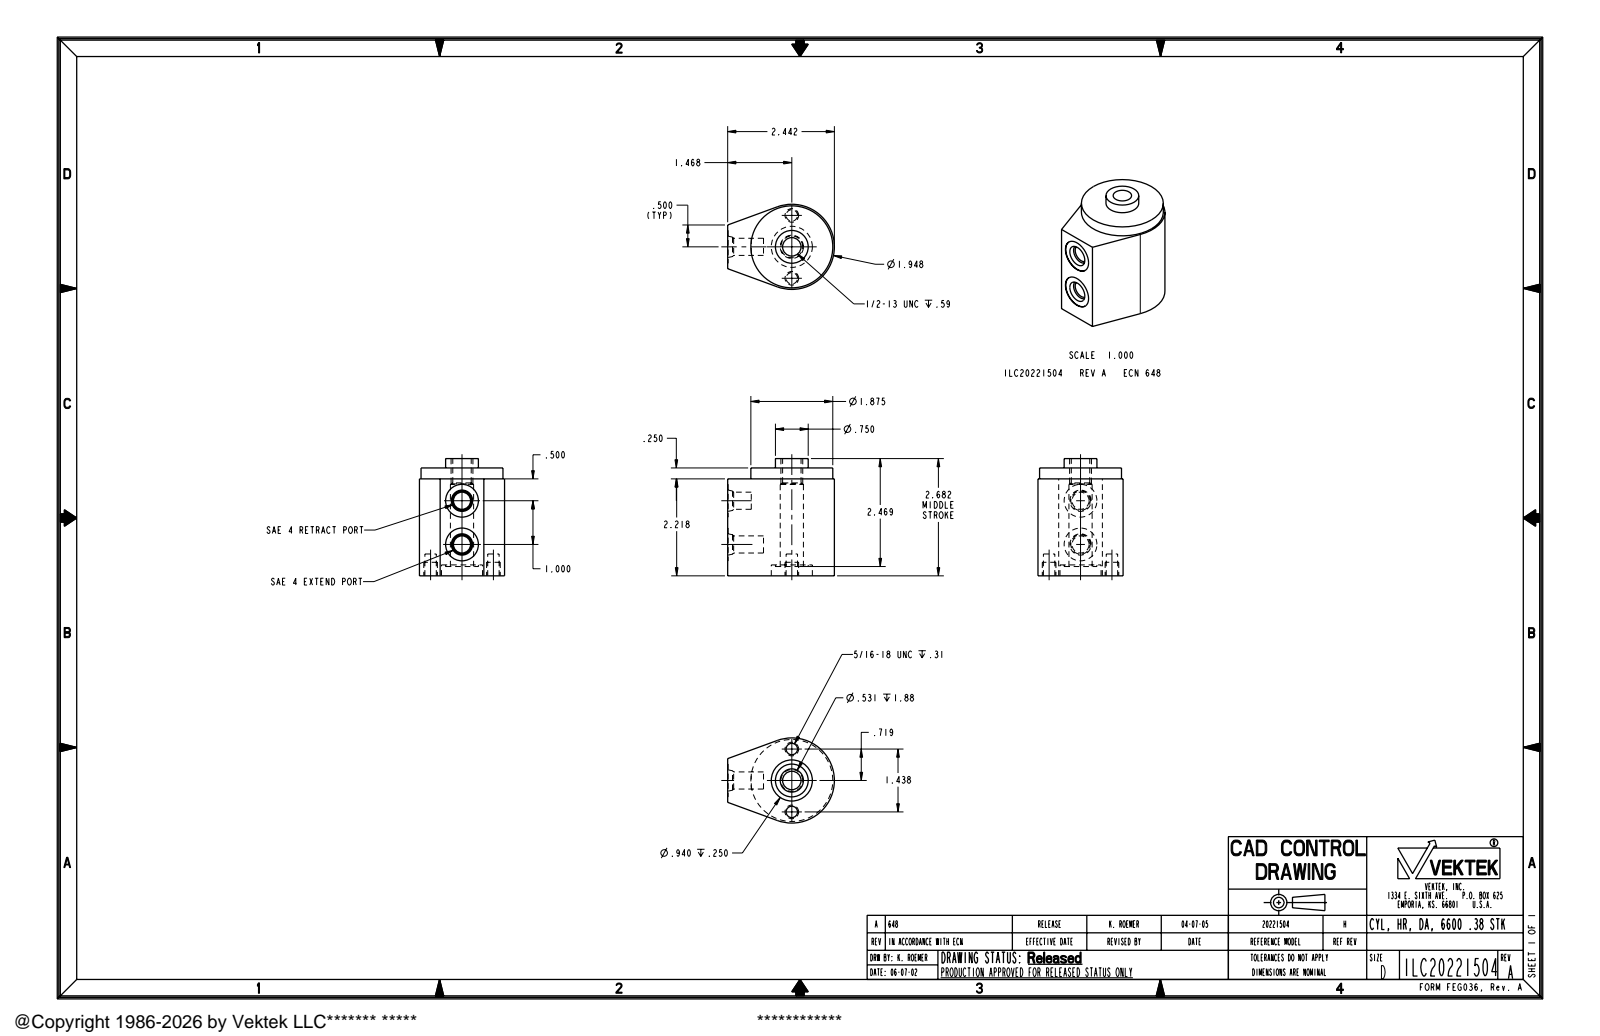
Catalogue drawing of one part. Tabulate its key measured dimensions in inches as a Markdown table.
| quantity | value |
| --- | --- |
| part name | ILC20221504 |
| STEP written by | PRO/ENGINEER BY PARAMETRIC TECHNOLOGY CORPORATION, 2004290 (AUTOMOTIVE_DESIGN_CC2) |
| units | inches |
| bodies | 1 solid, 58 faces (17 planar, 31 cylindrical, 10 other) |
| overall size | 2.682 × 2.442 × 1.948 |
| volume | 8.171 in³ |
| surface area | 33.78 in² |
| round holes (diameter × count) | 0.261 × 2, 0.392 × 2, 0.75 × 2, 0.422 × 1, 0.531 × 1, 0.94 × 1 |
| round bosses / shafts (diameter × count) | 0.312 × 2, 1.875 × 1, 0.75 × 1, 0.5 × 1 |
| partial cylindrical surfaces (radius × count) | 0.974 × 1 |
| main face-to-face distances | 2.468, 0.25, 2.218, 1.968, 2.682, 0.464, 0.214, 2.432, 0.213, 0.037 |
| hole center spacings | 0.719, 1, 1.438 |
